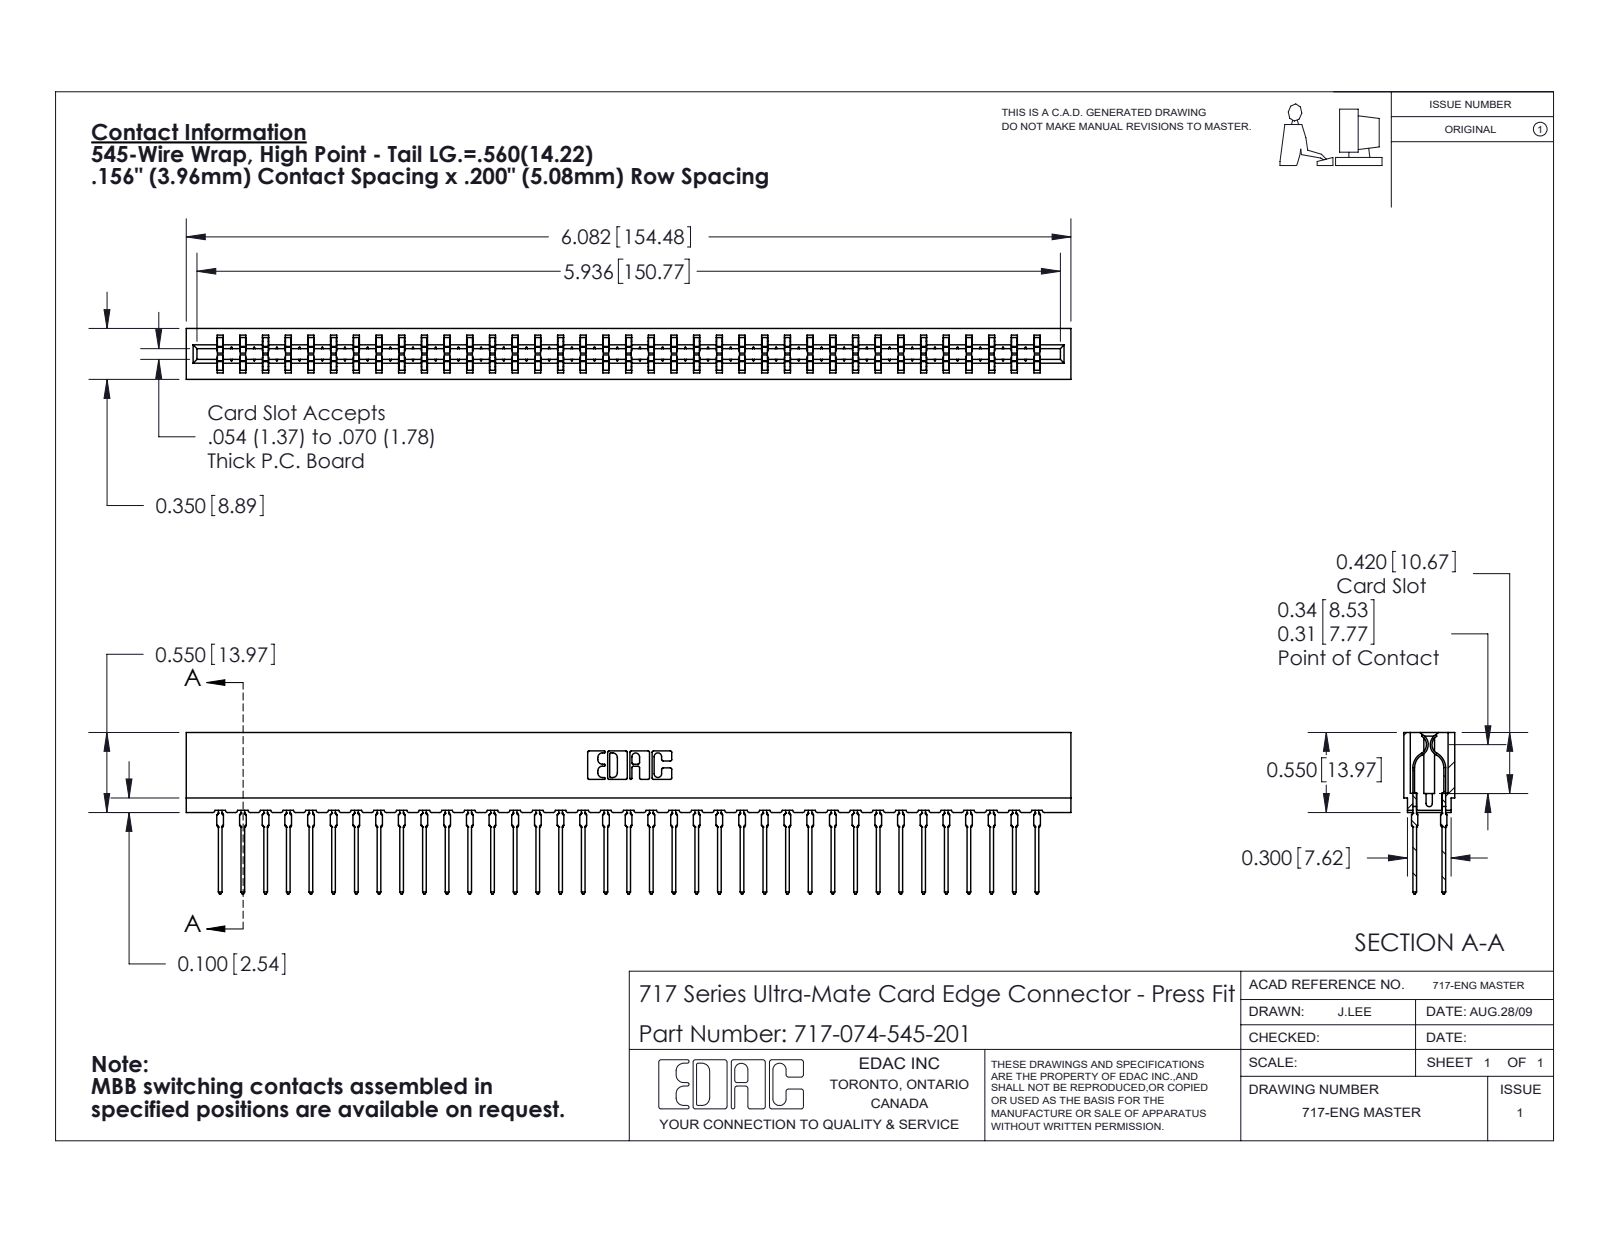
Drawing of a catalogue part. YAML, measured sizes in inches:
part_name: "717 Part_Insulator Option - 06; 717-074-545-201; 745-292-001_545"
step_written_by: "SolidWorks 2020 (CONFIG_CONTROL_DESIGN)"
units: inches
bodies: {solids: 75, faces: 6754, planar: 3495, cylindrical: 1335, other: 1924}
overall_size: [6.082, 1.109, 0.35]
volume: 0.834
surface_area: 34.25
partial_cylinders:
  - {radius: 0.021, count: 148}
  - {radius: 0.015, count: 74}
  - {radius: 0.01, count: 22}
  - {radius: 0.005, count: 8}
  - {radius: 0.011, count: 8}
  - {radius: 0.007, count: 6}
  - {radius: 0.031, count: 6}
  - {radius: 0.026, count: 3}
face_to_face_distances: [0.212, 0.138, 0.35, 0.063, 0.287, 0.076, 0.149, 0.074, 0.087, 0.263]
